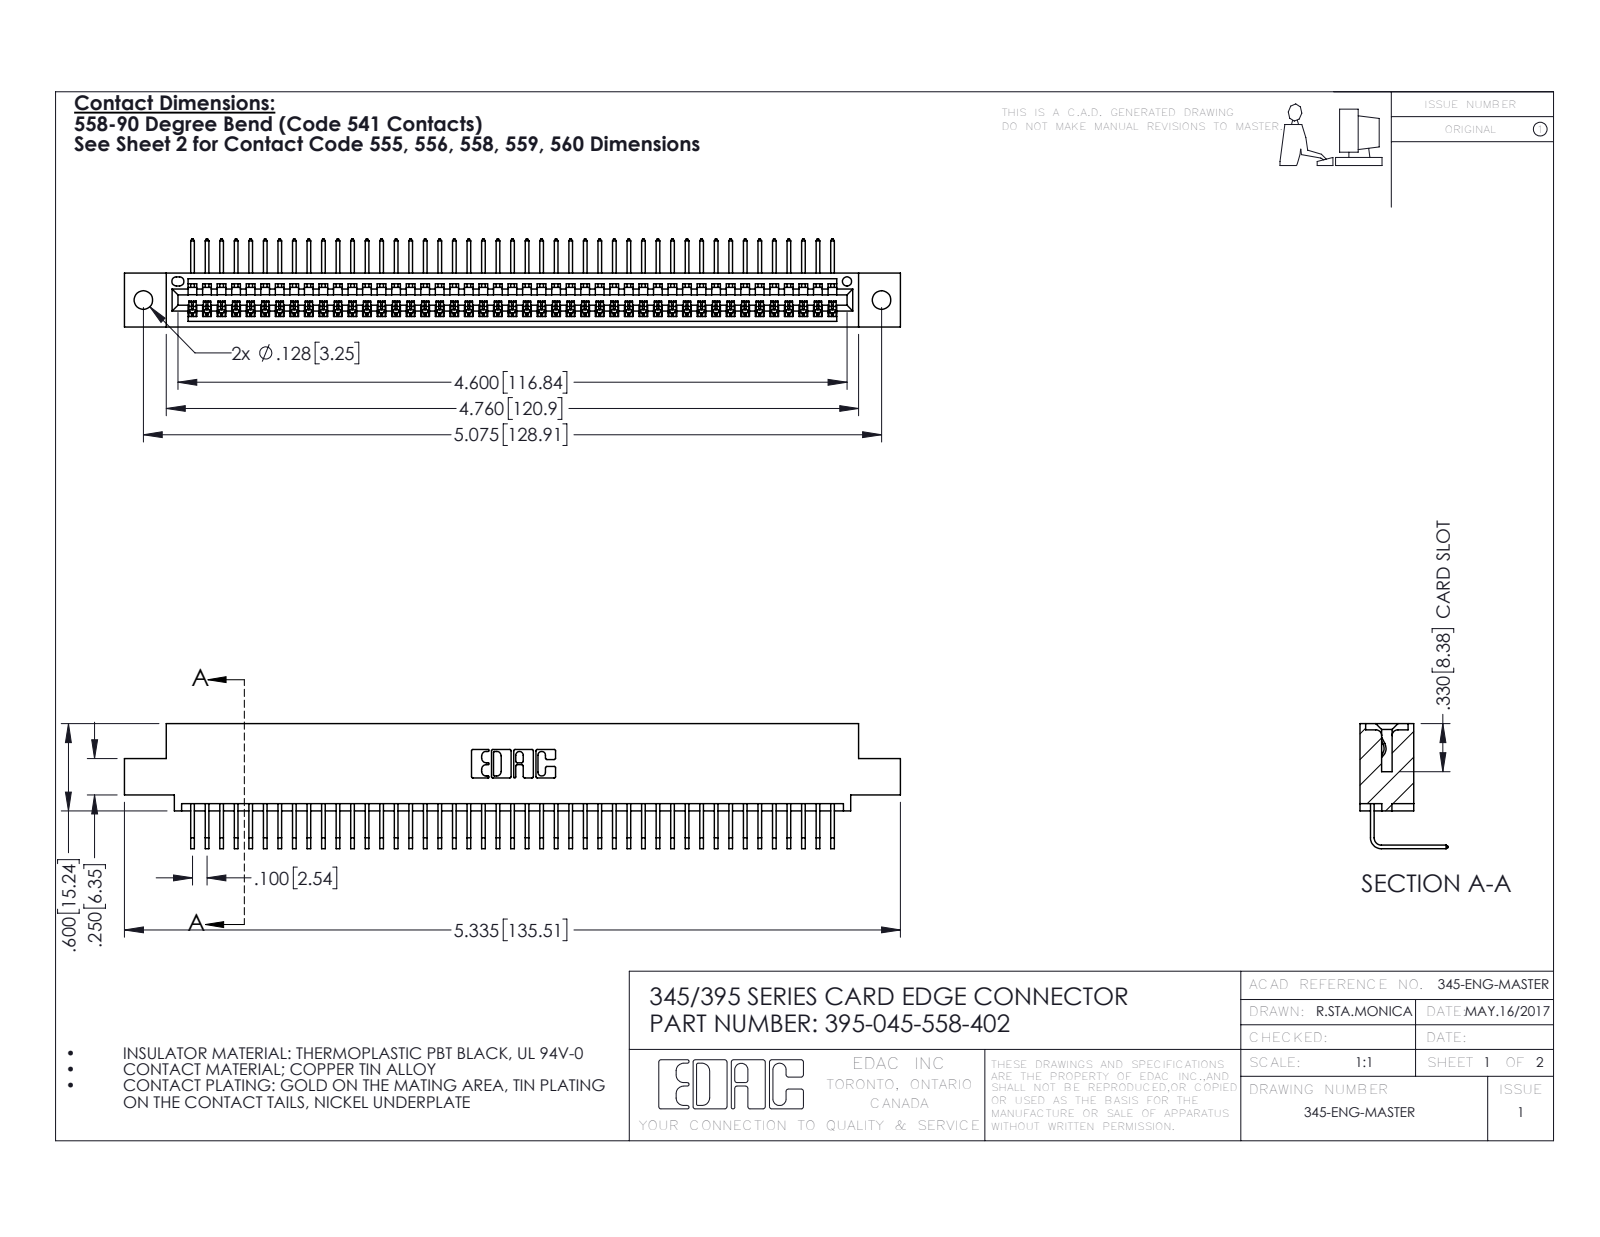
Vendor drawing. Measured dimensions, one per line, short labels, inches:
name: 345-292-001_558 Tail - 2; 345 Part_0.110 Offset - 0.128 Dia; 395-045-558-402
written by: SolidWorks 2016 (CONFIG_CONTROL_DESIGN)
unit: in
bodies: 46 solids, 2830 faces (1974 planar, 856 cylindrical, 0 other)
size: 5.335 × 0.859 × 0.605
volume: 0.789 in³; area: 27.78 in²
holes: 2× ⌀0.128, 1× ⌀0.064
rounds: 90× R0.006, 22× R0.01, 6× R0.007, 6× R0.031, 3× R0.026, 2× R0.031, 2× R0.04, 1× R0.014
face distances: 0.072, 0.298, 0.37, 0.2, 0.098, 0.272, 0.025, 0.225, 0.149, 0.072
hole spacings: 0.27, 4.839, 5.075
